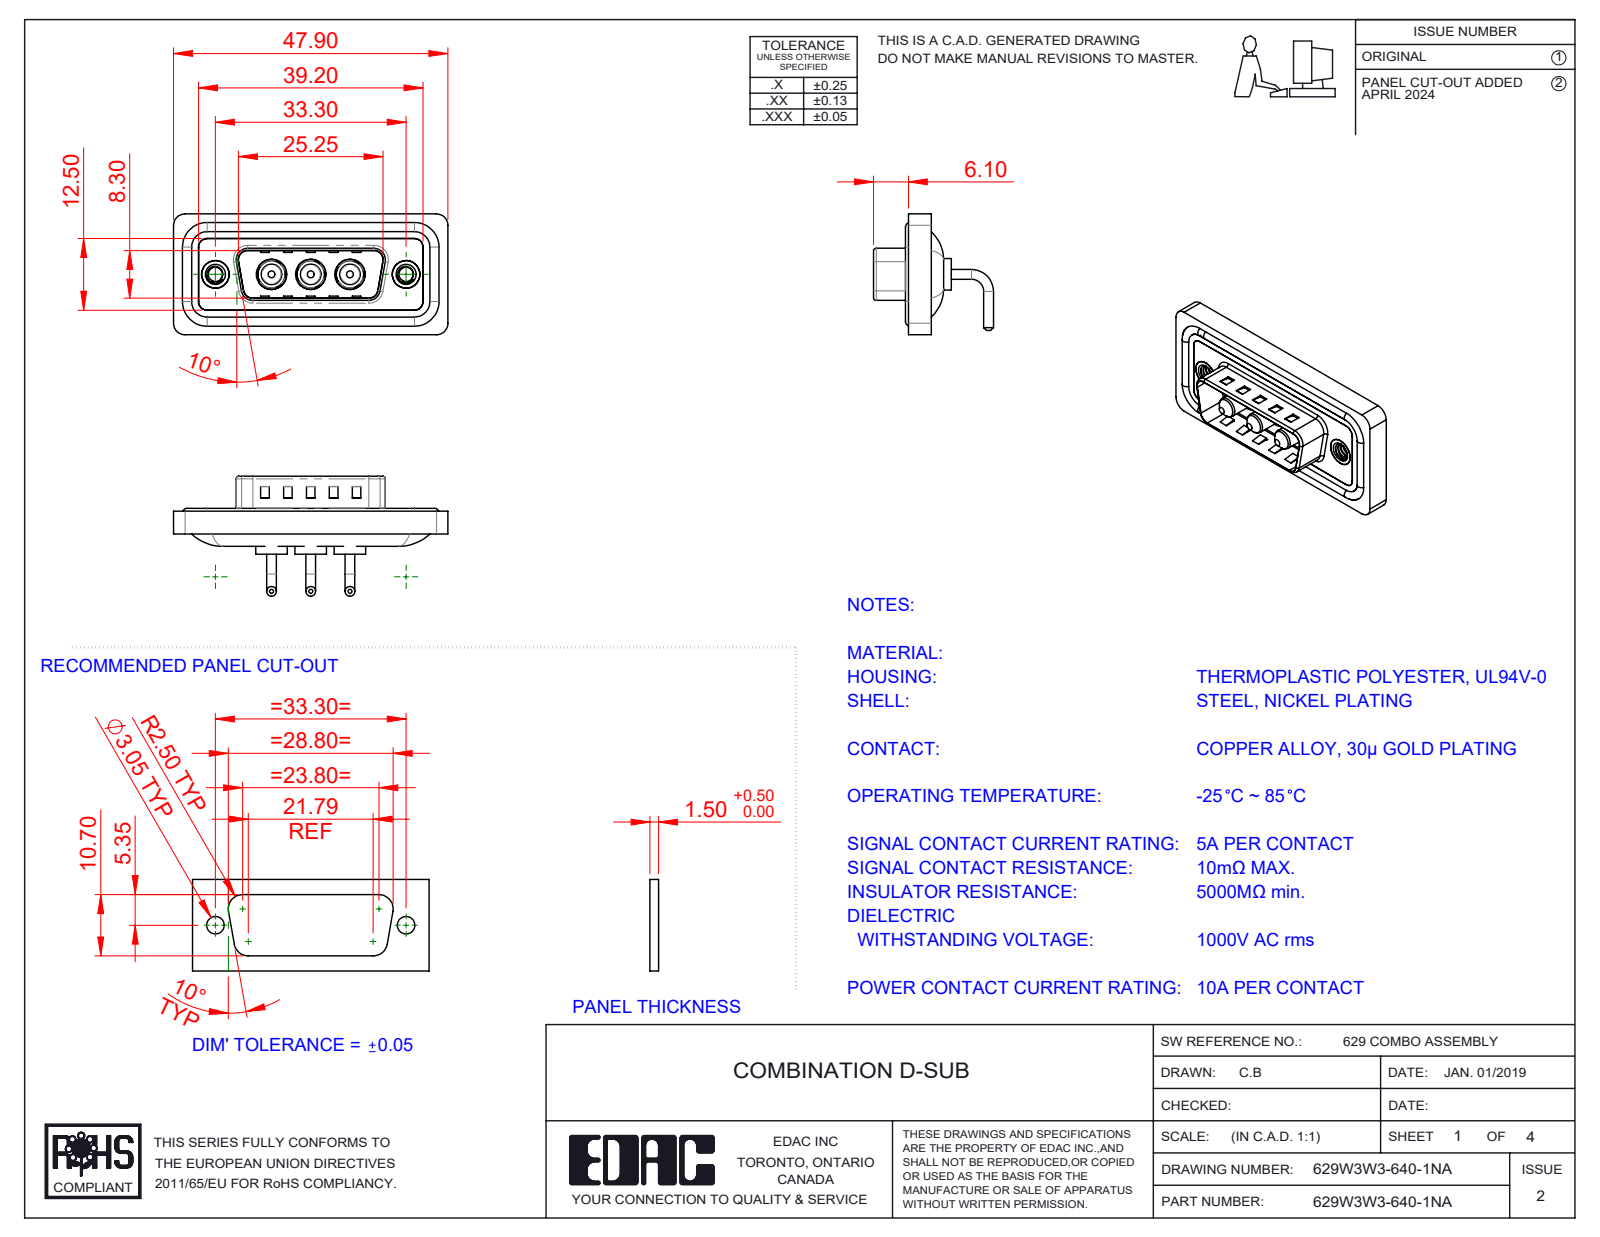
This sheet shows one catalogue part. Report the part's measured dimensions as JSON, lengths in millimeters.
{"part_name": "629Combo Waterproof Housing_15 Contacts; 629Combo Housing_3W3; Power Pin_10A RA; 629Combo Shell Rear_15 Contacts (+3 more)", "step_written_by": "SolidWorks 2023 (CONFIG_CONTROL_DESIGN)", "units": "millimeters", "bodies": {"solids": 13, "faces": 570, "planar": 207, "cylindrical": 245, "other": 118}, "overall_size": [47.9, 21.1, 20.95], "volume_mm3": 5608, "surface_area_mm2": 8887, "round_holes": [[4.85, 3], [5.3, 3], [2.5, 2], [4, 2], [4.8, 2], [5, 2]], "round_bosses_or_shafts": [[1.7, 6], [1.6, 4], [5.5, 3], [5.2, 3], [4.75, 3], [3.75, 3], [3.6, 3], [4.9, 2]], "partial_cylinders_radius": [[2, 20], [1.5, 18], [0.5, 8], [1.6, 8], [0.25, 4], [0.6, 4], [0.65, 4], [0.9, 4]], "face_to_face_distances": [0.4, 2.9, 0.8, 1.1, 2.1, 1.6, 3.1, 2.5, 4.5, 1.5], "hole_center_spacings": [6.85, 9.8, 16.65, 23.5, 13.7, 33.3]}
